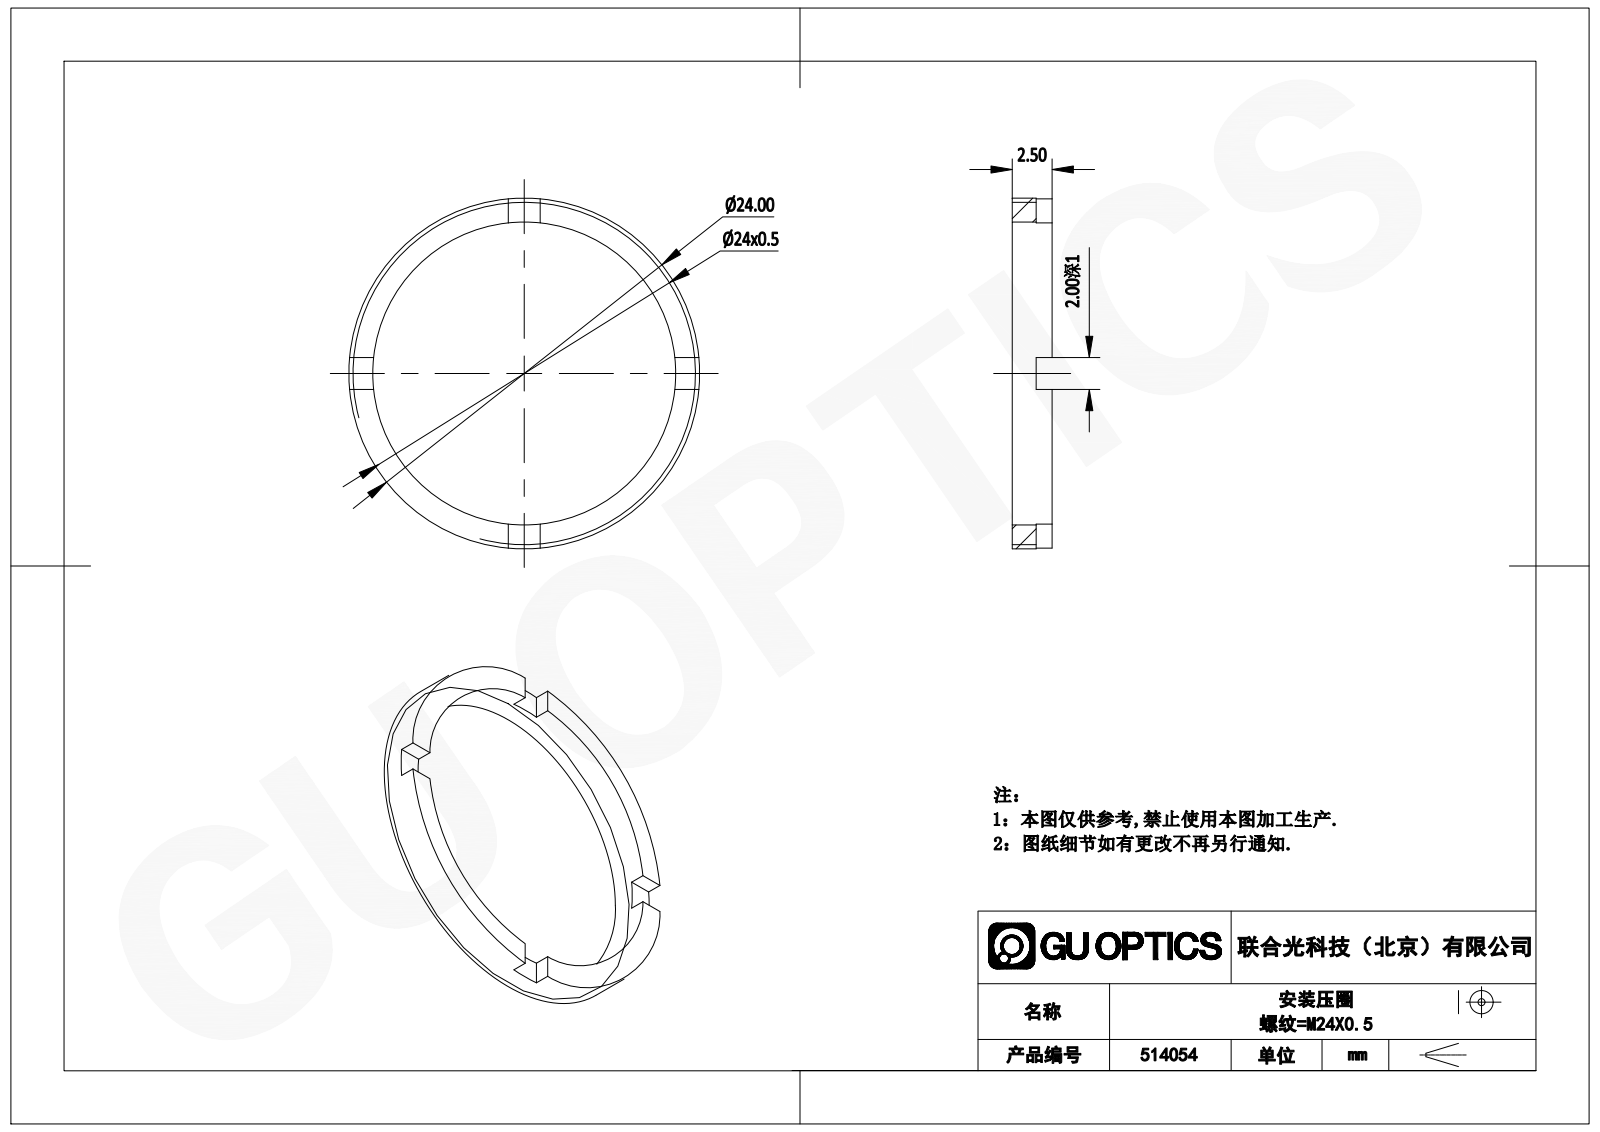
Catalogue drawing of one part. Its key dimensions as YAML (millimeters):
part_name: "514054"
step_written_by: "SolidWorks 2020 (CONFIG_CONTROL_DESIGN)"
units: millimeters
bodies: {solids: 1, faces: 21, planar: 17, cylindrical: 4, other: 0}
overall_size: [24, 24, 2.5]
volume: 253
surface_area: 562
round_holes:
  - {diameter: 21, count: 1}
round_bosses_or_shafts:
  - {diameter: 24, count: 1}
face_to_face_distances: [2.5, 1.5, 1, 2]
